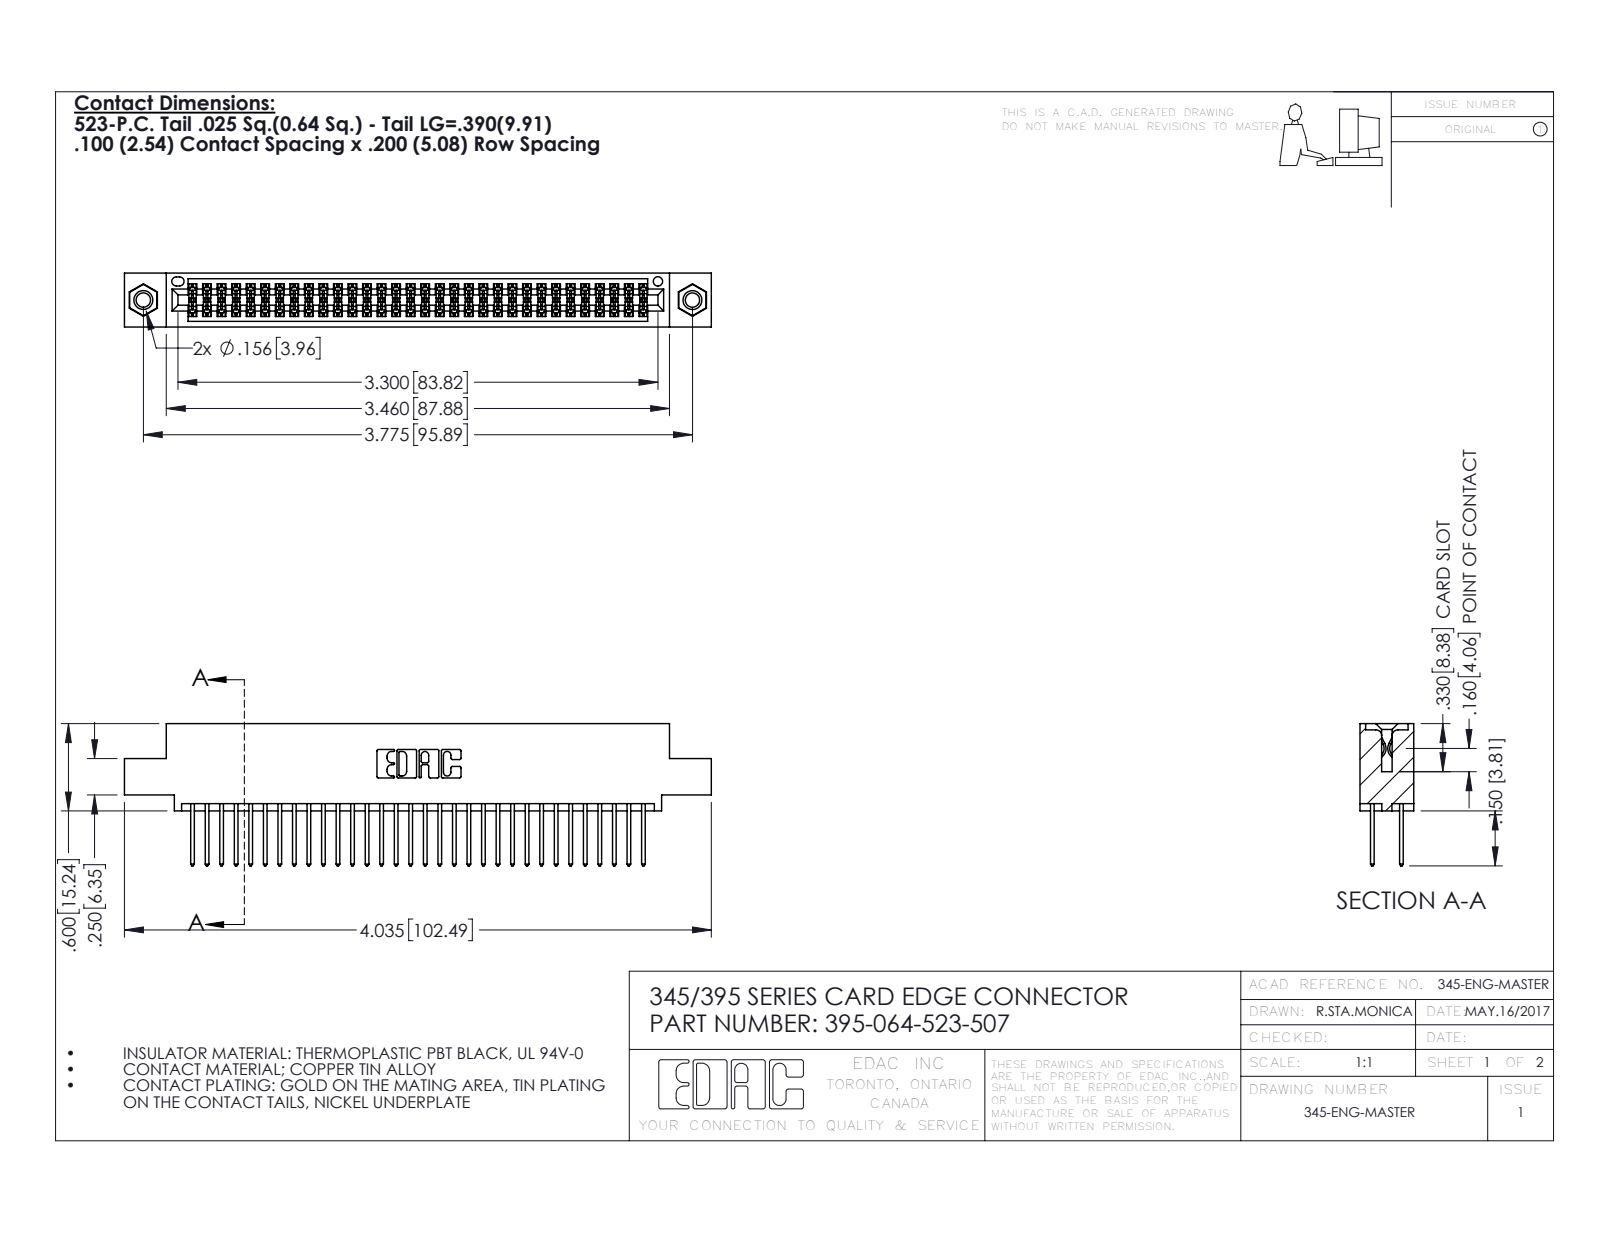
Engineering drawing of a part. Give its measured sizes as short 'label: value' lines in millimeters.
name: 345-250-001_345-250-005-103; 345-292-001_345-293-123; 395-064-523-507; 345 Part_0.110 Offset - 0.156 Dia-TI
written by: SolidWorks 2016 (CONFIG_CONTROL_DESIGN)
unit: mm
bodies: 67 solids, 3390 faces (2228 planar, 1146 cylindrical, 16 other)
size: 102.5 × 24.8 × 9.4
volume: 9 910 mm³; area: 15 160 mm²
holes: 2× ⌀2.5, 2× ⌀3.2, 2× ⌀4, 1× ⌀1.6
bosses: 2× ⌀3.9
rounds: 96× R0.2, 64× R0.3, 22× R0.3, 6× R0.2, 6× R0.8, 3× R0.7, 2× R0.4, 2× R0.5
face distances: 1.8, 7.6, 5.1, 2.5, 6.9, 0.6, 9.4, 5.7, 4.4, 3.8
hole spacings: 6.9, 89.9, 95.9
